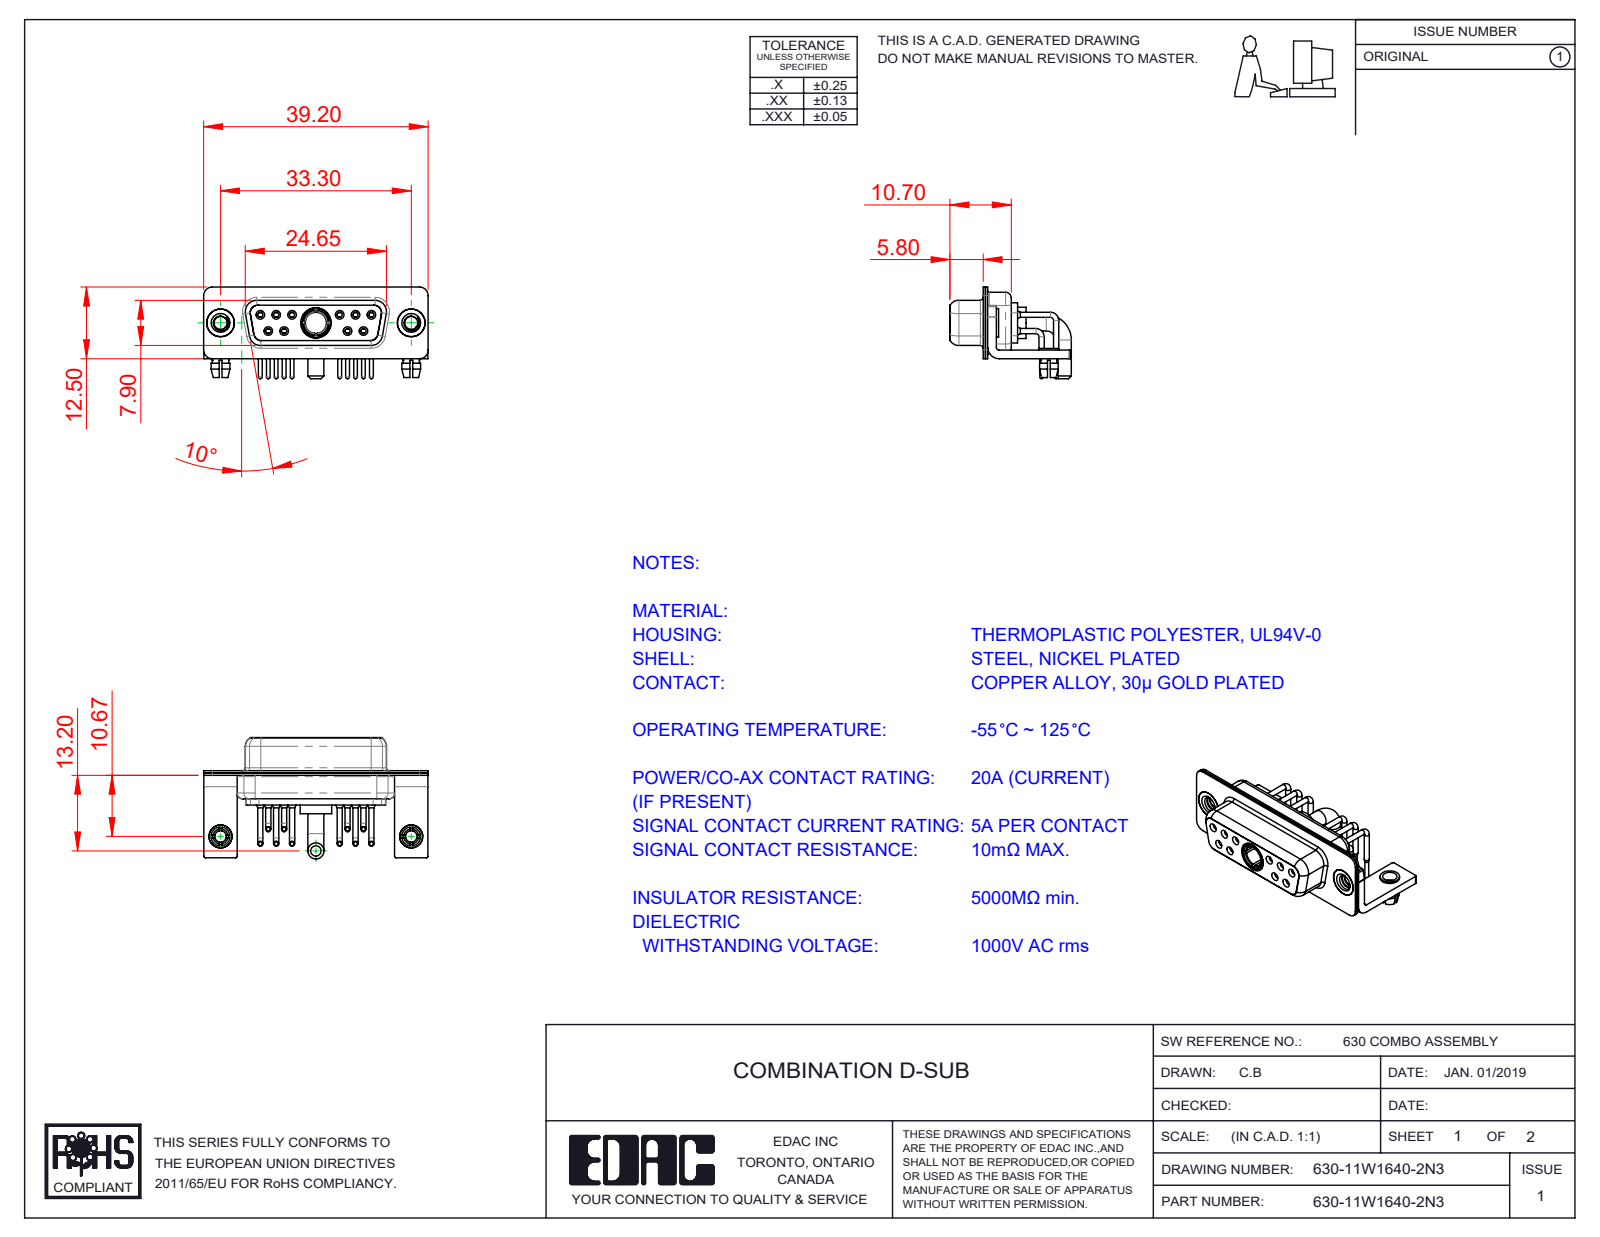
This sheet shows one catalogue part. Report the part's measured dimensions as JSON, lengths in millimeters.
{"part_name": "Power Socket_20A RA; 630Combo Stabilizer Bracket; 630Combo Board Lock; 630Combo Contact Row 1 (+6 more)", "step_written_by": "SolidWorks 2020 (CONFIG_CONTROL_DESIGN)", "units": "millimeters", "bodies": {"solids": 21, "faces": 1019, "planar": 314, "cylindrical": 442, "other": 263}, "overall_size": [39.2, 21.2, 16], "volume_mm3": 2950, "surface_area_mm2": 7069, "round_holes": [[2, 12], [0.9, 10], [1.1, 10], [1.5, 10], [1.7, 6], [1.6, 4], [4.85, 3], [2.26, 2], [2.5, 2], [3.2, 2], [4, 2], [4.05, 2]], "round_bosses_or_shafts": [[0.9, 10], [0.65, 10], [1.6, 6], [5, 2], [4.95, 2], [4.8, 2], [4, 2], [3.4, 2]], "partial_cylinders_radius": [[0.25, 16], [1.5, 16], [2, 13], [1.35, 12], [1.6, 8], [0.5, 5], [0.6, 4], [0.65, 4]], "face_to_face_distances": [0.4, 0.8, 0.45, 1.4, 8.45, 1.5, 1.8, 8.9, 6.2, 2.3], "hole_center_spacings": [3.16, 2.77, 13.85, 11.08, 16.62, 5.03, 5.04, 5.54]}
